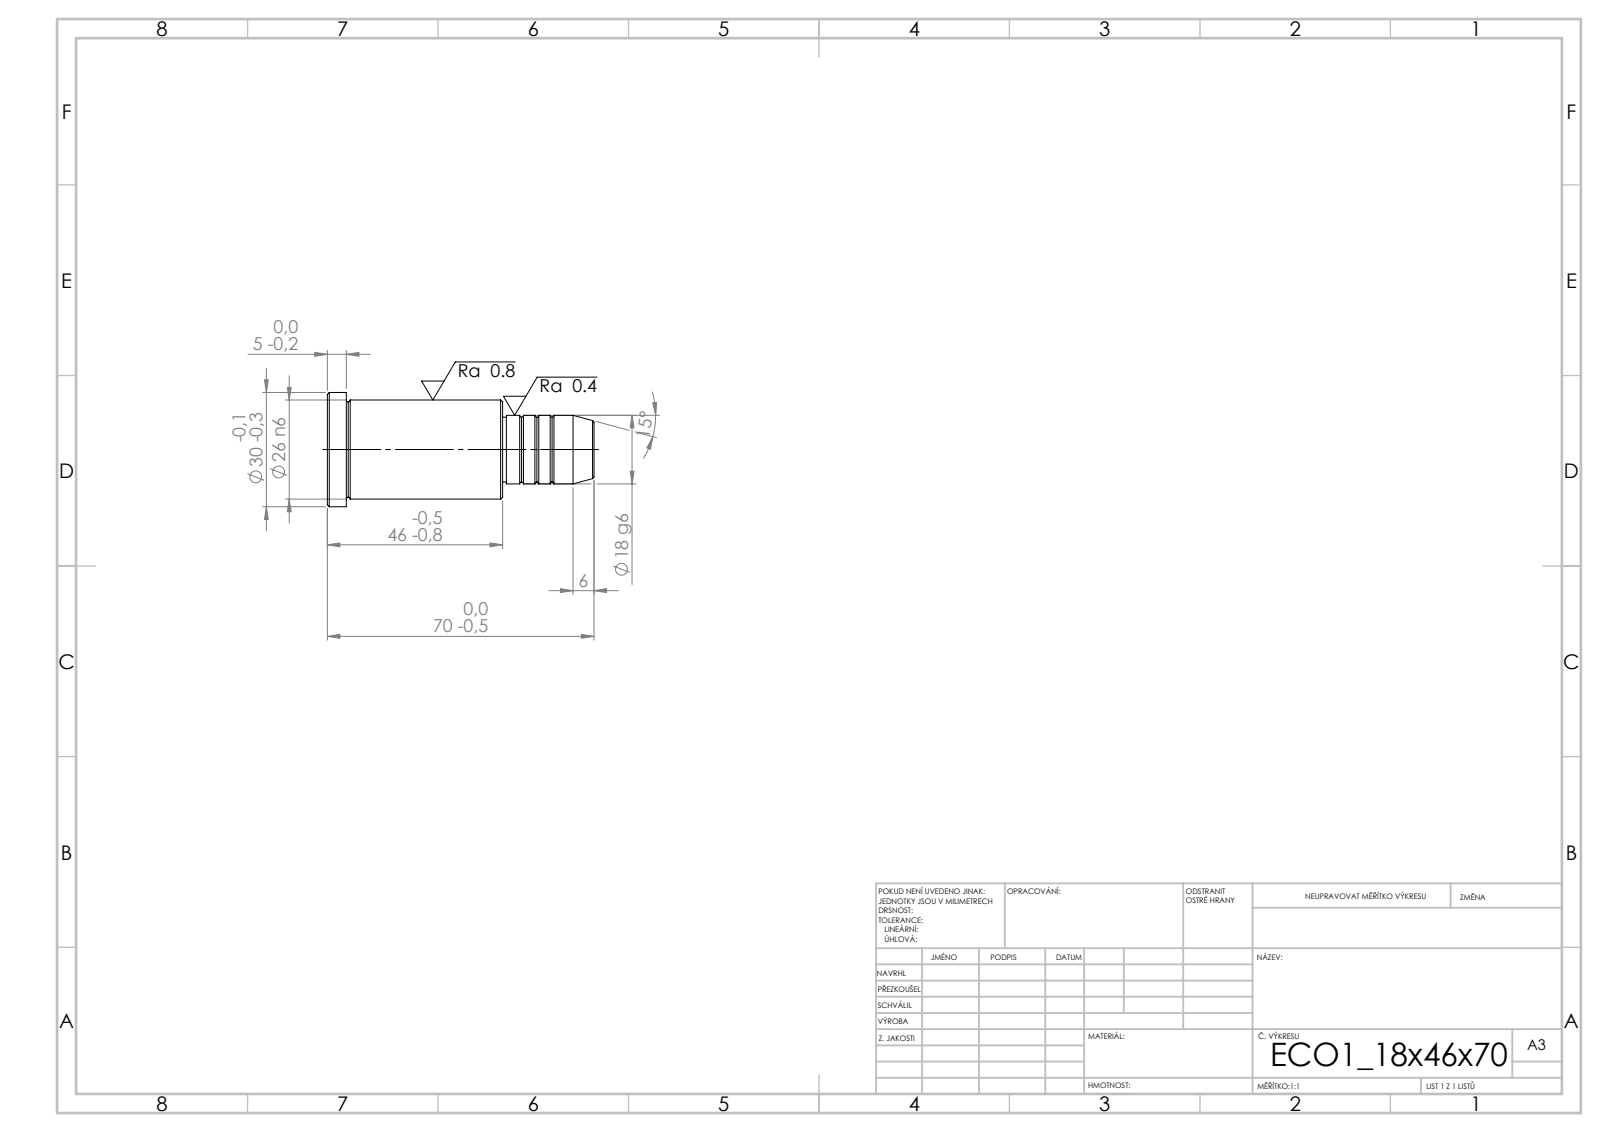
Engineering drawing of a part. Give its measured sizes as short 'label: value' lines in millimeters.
written by: SolidWorks 2019 (CONFIG_CONTROL_DESIGN)
unit: mm
bodies: 1 solid, 43 faces (5 planar, 14 cylindrical, 24 other)
size: 70 × 30 × 30
volume: 31 046 mm³; area: 6 624 mm²
bosses: 1× ⌀30, 1× ⌀26, 1× ⌀18, 1× ⌀17
face distances: 46, 41, 5, 24, 65, 70, 23, 1, 42, 47
